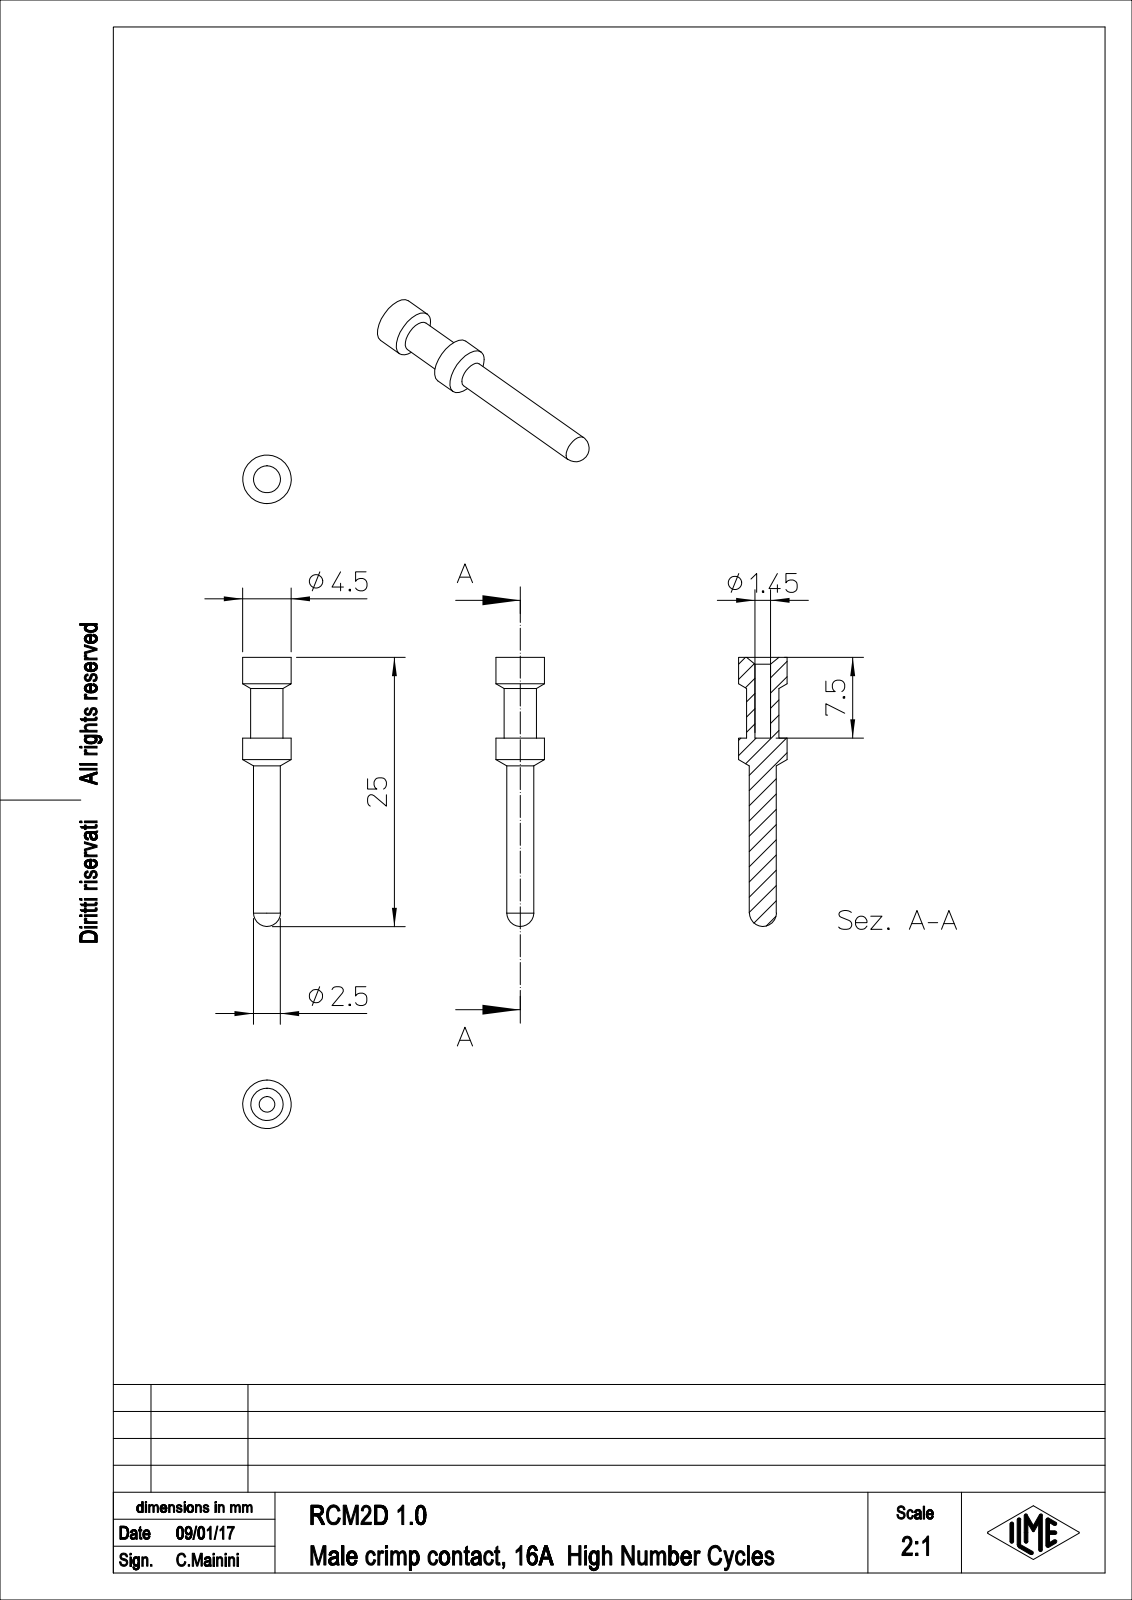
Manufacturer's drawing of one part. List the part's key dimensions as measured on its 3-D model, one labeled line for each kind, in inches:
Part name (STEP PRODUCT): RCM2D_1.0
STEP written by: PTC Creo Elements/Direct Modeling 19.0E 27-Jun-2016 (C) Parametric Technology GmbH (AUTOMOTIVE_DESIGN)
Units: inches
Bodies: 1 solid, 21 faces (3 planar, 10 cylindrical, 8 other)
Overall size (bounding box): 0.984 × 0.177 × 0.177
Volume: 0.01 in³ · Surface area: 0.471 in²
Round holes (diameter × count): ⌀0.057 ×1
Round bosses / shafts (diameter × count): ⌀0.177 ×1, ⌀0.118 ×1, ⌀0.098 ×1
Main face-to-face distances: 0.295
